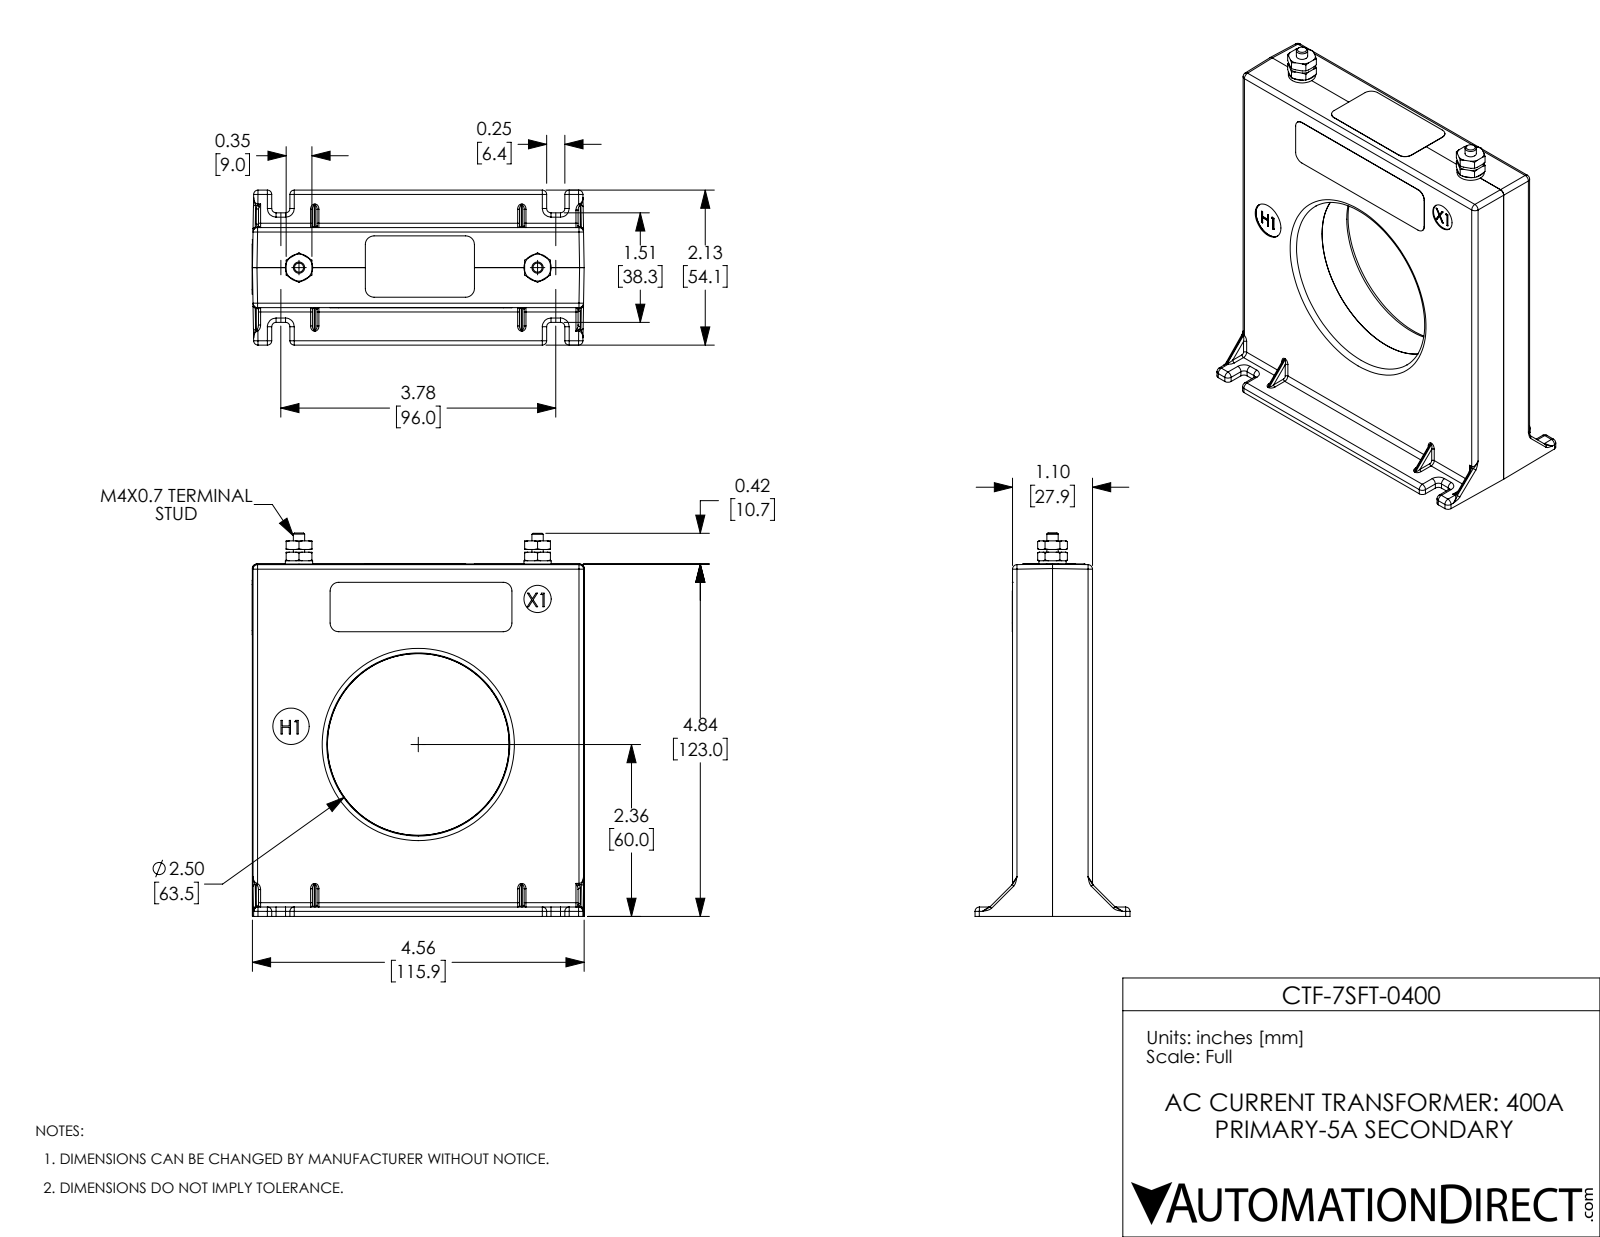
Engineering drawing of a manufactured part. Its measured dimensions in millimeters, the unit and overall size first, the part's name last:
Units: millimetres
Overall size (bounding box): 133.9 × 117 × 54.1
Round holes (diameter × count): ⌀3.9 ×2, ⌀4.2 ×2, ⌀9.5 ×1, ⌀12.7 ×1
Round bosses / shafts (diameter × count): ⌀9.5 ×2
Partial cylindrical surfaces — rounded edges, fillets, slot ends (radius × count): R1.5 ×37, R0.6 ×25, R0.8 ×18, R1.6 ×5, R1.6 ×5, R3 ×5
Main face-to-face distances: 14, 27.9, 115.8, 3.3, 14, 28, 123, 119.7, 123.1, 119.8
Hole centre spacings: 83.3, 96.9
Volume: 318 100 mm³ · Surface area: 74 710 mm²
Bodies: 14 solids, 467 faces (172 planar, 143 cylindrical, 152 other)
Part name (STEP PRODUCT): CTF-7SFT-0400
STEP written by: SolidWorks 2018 (AUTOMOTIVE_DESIGN)
